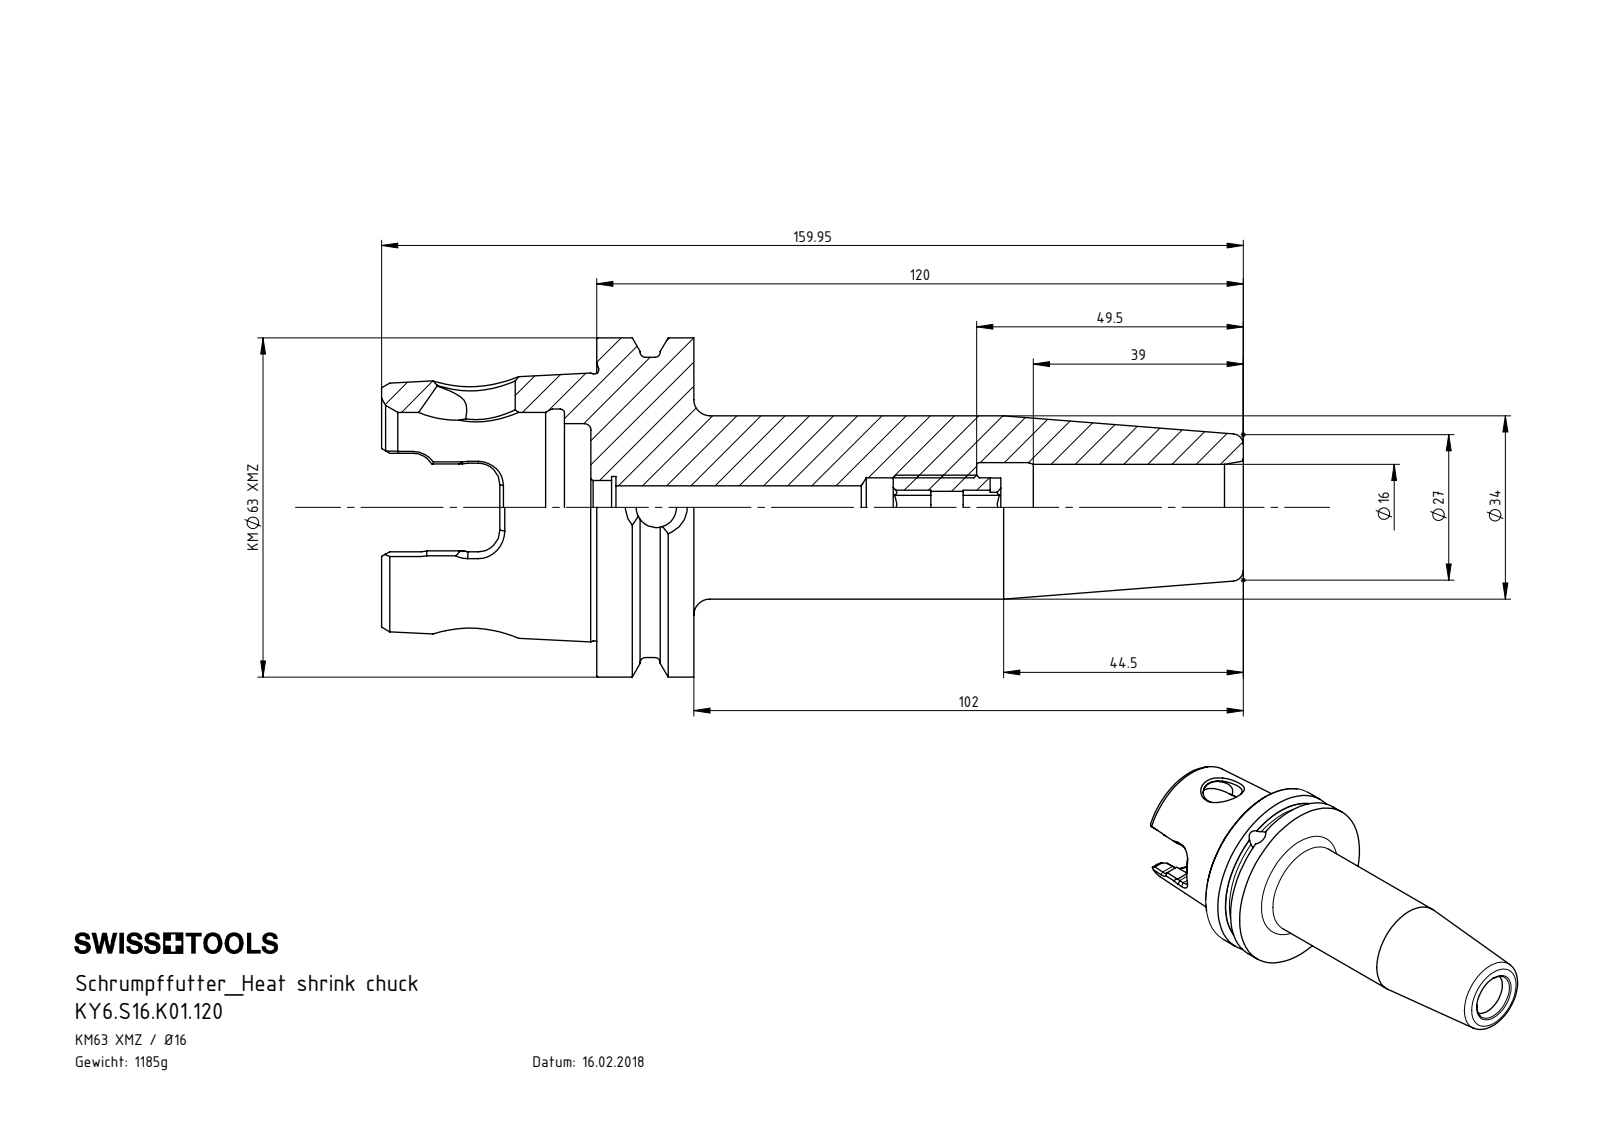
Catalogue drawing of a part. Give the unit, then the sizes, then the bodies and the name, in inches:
Units: inches
Overall size (bounding box): 6.297 × 2.478 × 2.478
Round holes (diameter × count): ⌀0.294 ×2, ⌀0.236 ×1, ⌀0.315 ×1, ⌀0.334 ×1, ⌀0.394 ×1, ⌀0.433 ×1, ⌀0.453 ×1, ⌀0.571 ×1, ⌀0.63 ×1, ⌀0.654 ×1, ⌀1.224 ×1, ⌀1.389 ×1
Round bosses / shafts (diameter × count): ⌀2.478 ×1, ⌀2.193 ×1, ⌀1.339 ×1, ⌀0.472 ×1
Partial cylindrical surfaces — rounded edges, fillets, slot ends (radius × count): R0.157 ×6, R0.277 ×2
Main face-to-face distances: 0.709, 0.043, 0.752, 0.236, 0.193, 0.945, 1.337, 1.53, 1.573, 2.281
Volume: 9.215 in³ · Surface area: 54.71 in²
Bodies: 2 solids, 277 faces (79 planar, 60 cylindrical, 138 other)
Part name (STEP PRODUCT): KY6.S16.K01.120; ERU-AN5.K01.020_A; KY6-S16.K01.120_A
STEP written by: SolidWorks 2017 (CONFIG_CONTROL_DESIGN)
